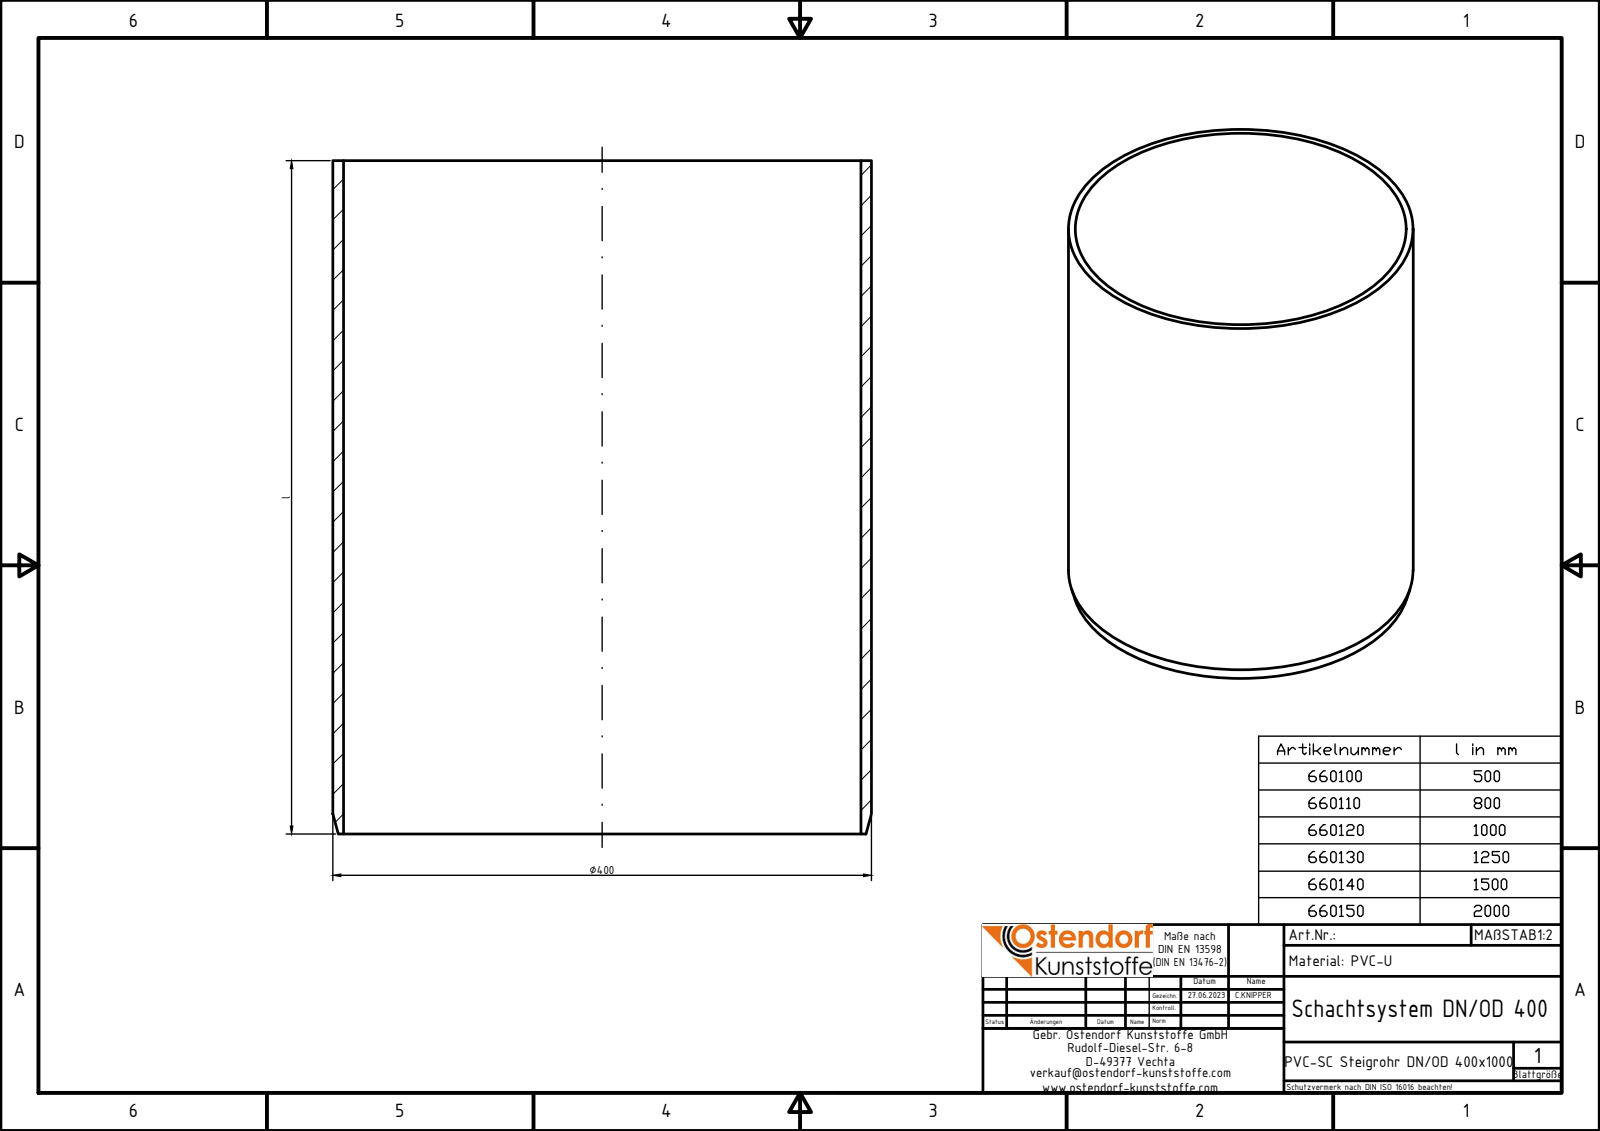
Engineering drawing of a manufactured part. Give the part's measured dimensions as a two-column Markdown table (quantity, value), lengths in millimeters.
| quantity | value |
| --- | --- |
| part name | 660120 |
| STEP written by | Autodesk Inventor 2020 (AUTOMOTIVE_DESIGN) |
| units | millimeters |
| bodies | 1 solid, 5 faces (2 planar, 2 cylindrical, 1 other) |
| overall size | 1000 × 400 × 400 |
| volume | 9 694 000 mm³ |
| surface area | 2 479 000 mm² |
| round holes (diameter × count) | 384.2 × 1 |
| round bosses / shafts (diameter × count) | 400 × 1 |
| main face-to-face distances | 1000 |
